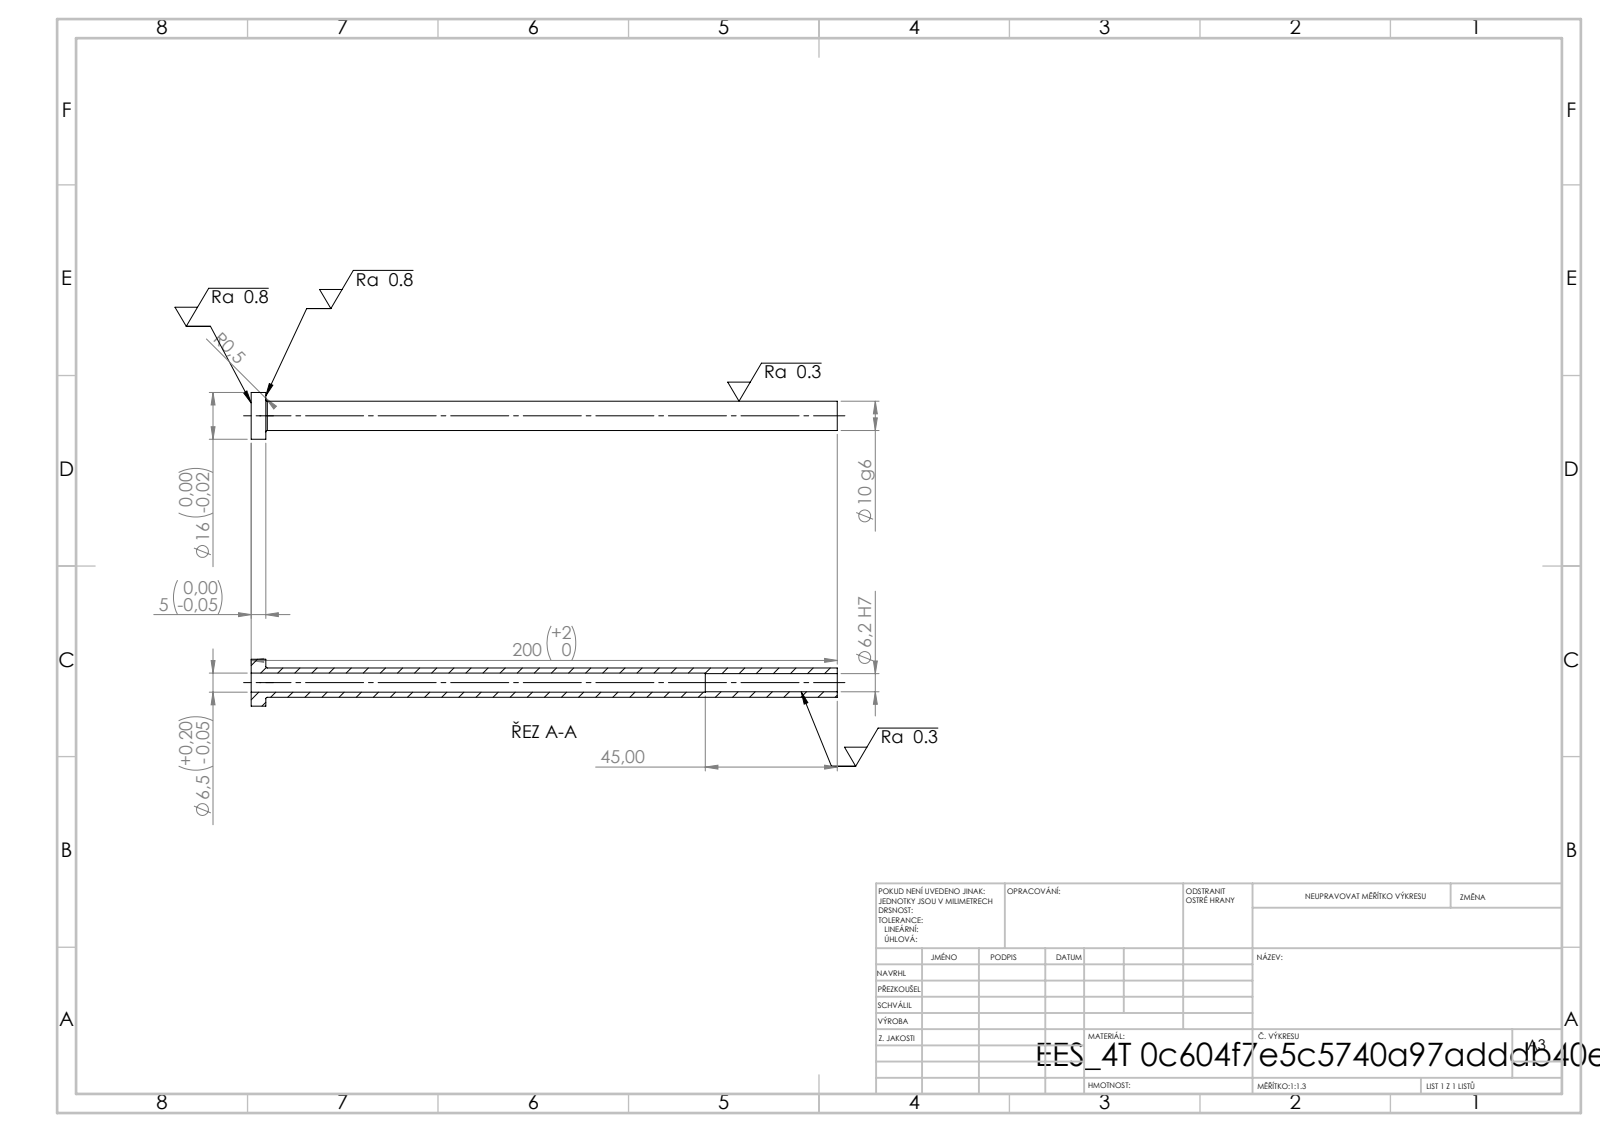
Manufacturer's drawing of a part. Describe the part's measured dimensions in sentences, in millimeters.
Its 3-D file was written by "SolidWorks 2019 (CONFIG_CONTROL_DESIGN)". It is 1 solid with 14 faces: 4 planar, 8 cylindrical and 2 other. Overall it measures 200 by 16 by 16 millimeters. Its volume is 9 820 cubic millimeters and its surface area 10 754 square millimeters. Round holes: 1 of diameter 6.2, 1 of diameter 6.5. Round bosses or shafts: 1 of diameter 16, 1 of diameter 10. The main face-to-face distances are 5, 200, 195, 155, 150, 45.
